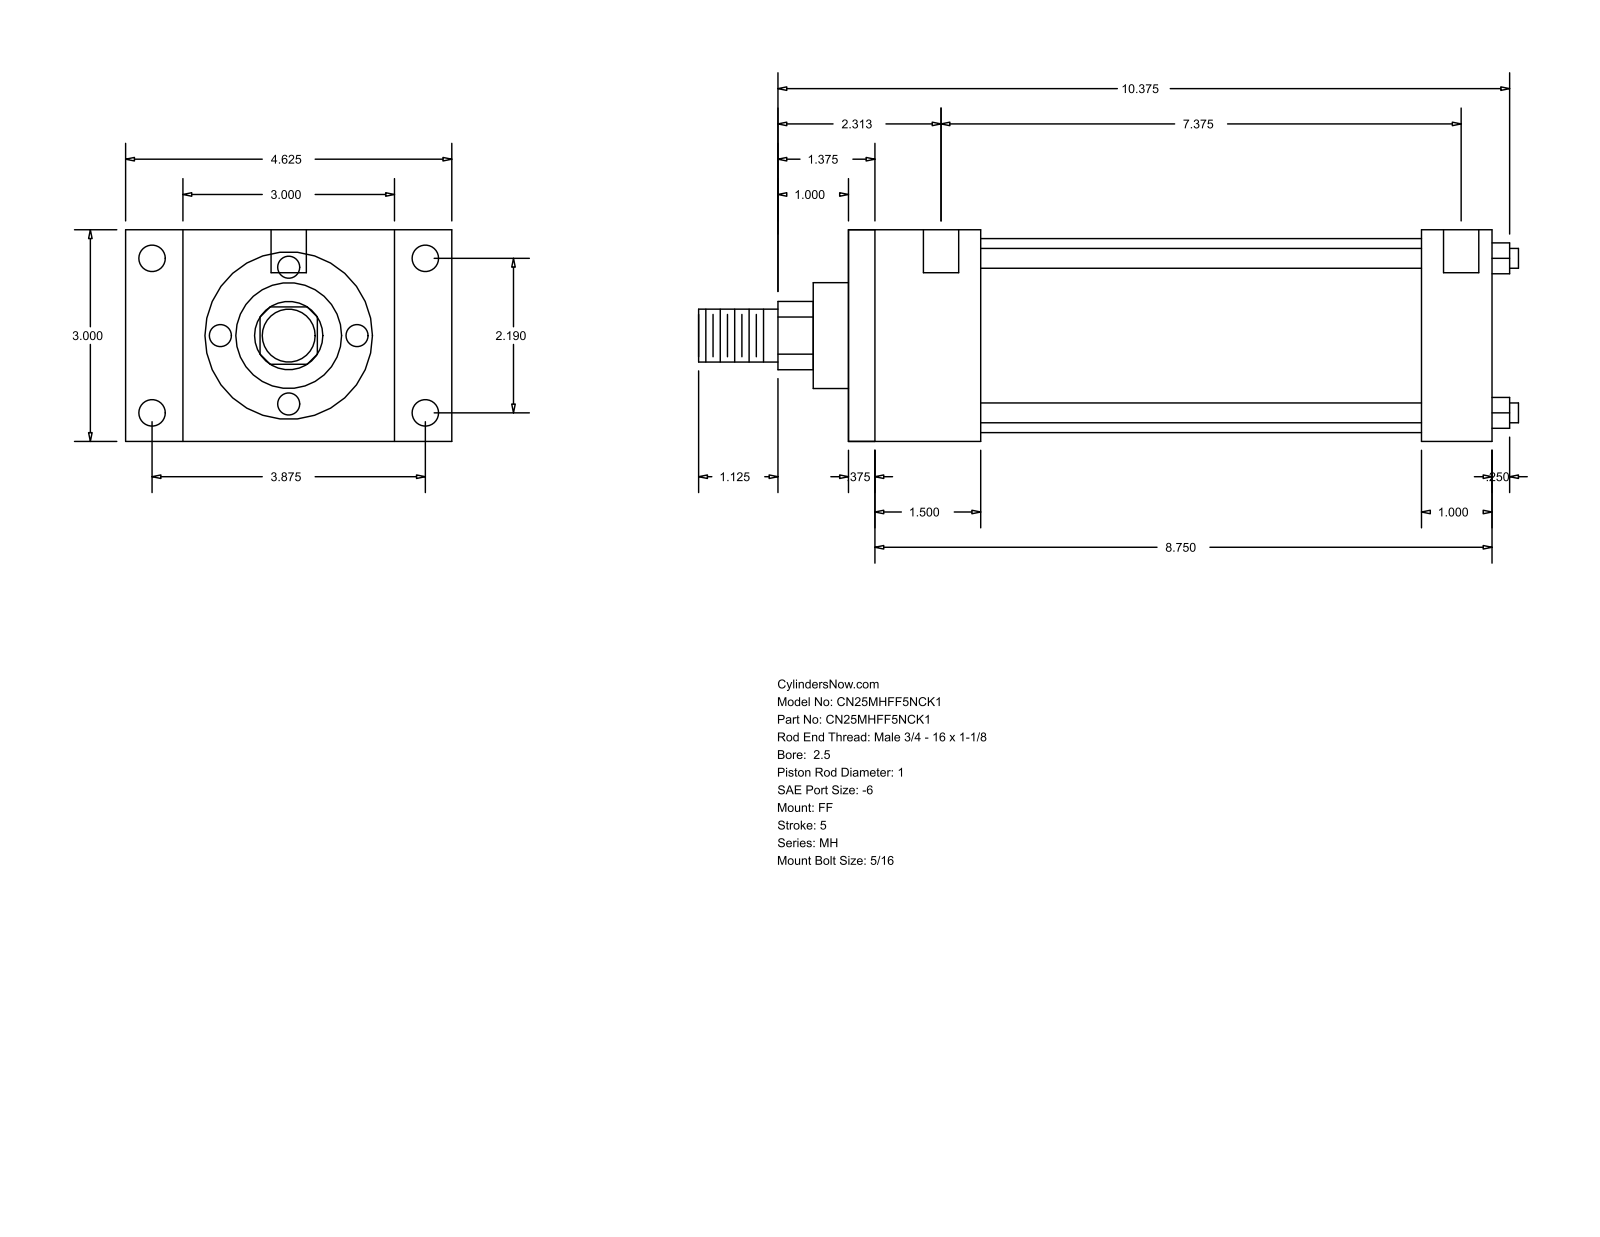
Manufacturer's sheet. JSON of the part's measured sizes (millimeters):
{"part_name": "MH_FF__0250_1", "step_written_by": "GSSL Pune (CONFIG_CONTROL_DESIGN)", "units": "millimeters", "bodies": {"solids": 0, "faces": 92, "planar": 64, "cylindrical": 28, "other": 0}, "overall_size": [295.27, 117.47, 76.2], "round_holes": [[5.56, 4], [9.53, 4], [12.7, 2]], "round_bosses_or_shafts": [[7.14, 4], [69.85, 1], [38.1, 1], [25.4, 1], [19.05, 1]], "partial_cylinders_radius": [[12.29, 1]], "face_to_face_distances": [76.2, 231.78, 9.52, 222.26, 25.4, 47.63, 206.38, 38.11, 196.86, 158.75], "hole_center_spacings": [55.62, 98.42, 113.05, 195.26, 3.18, 4.76, 187.32, 190.5]}
